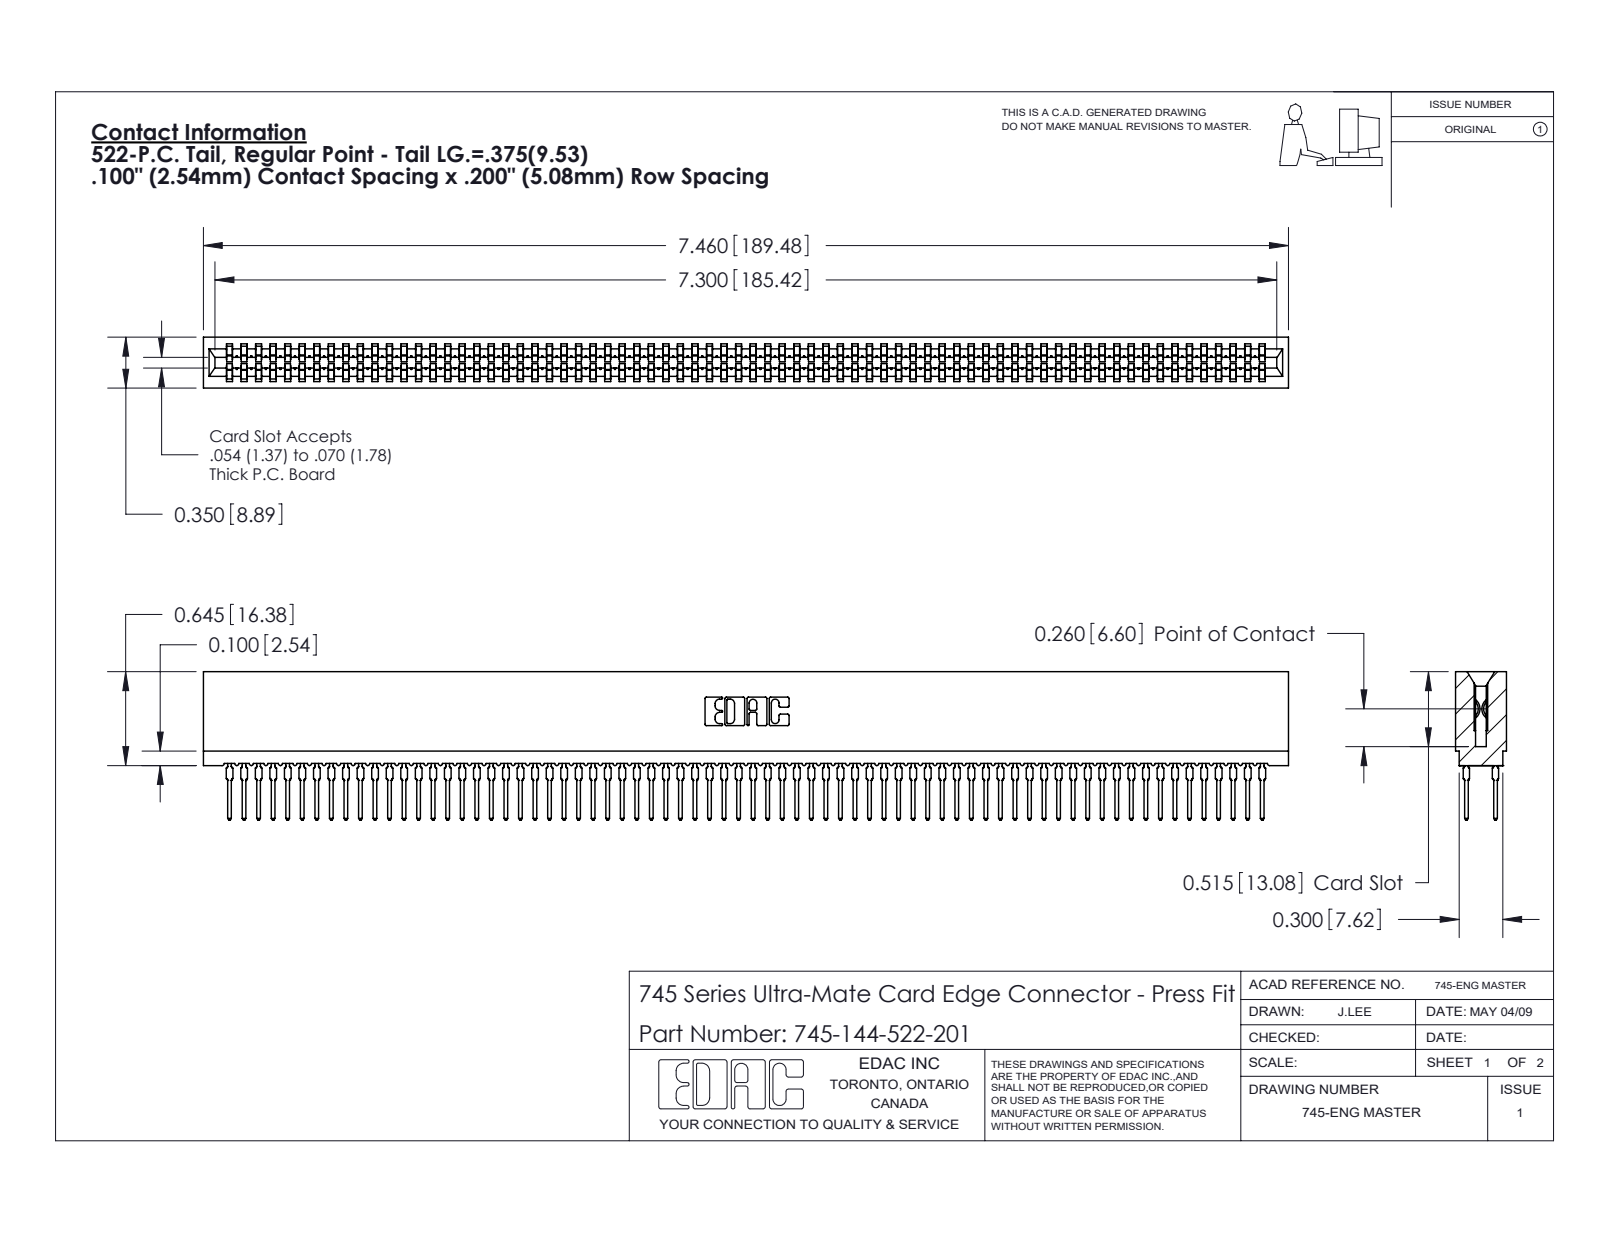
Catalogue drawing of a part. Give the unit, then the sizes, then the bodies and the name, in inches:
Units: inches
Overall size (bounding box): 7.46 × 1.021 × 0.35
Partial cylindrical surfaces — rounded edges, fillets, slot ends (radius × count): R0.021 ×288, R0.015 ×144, R0.01 ×22, R0.005 ×8, R0.011 ×8, R0.007 ×6, R0.031 ×6, R0.026 ×3
Main face-to-face distances: 0.35, 0.063, 0.287, 0.045, 0.305, 0.018, 0.243, 0.138, 0.212, 0.093
Volume: 1.04 in³ · Surface area: 55.53 in²
Bodies: 145 solids, 12983 faces (6679 planar, 2560 cylindrical, 3744 other)
Part name (STEP PRODUCT): 745-144-522-201; 745-292-001_522; 745 Part_Insulator Option - 01
STEP written by: SolidWorks 2020 (CONFIG_CONTROL_DESIGN)
